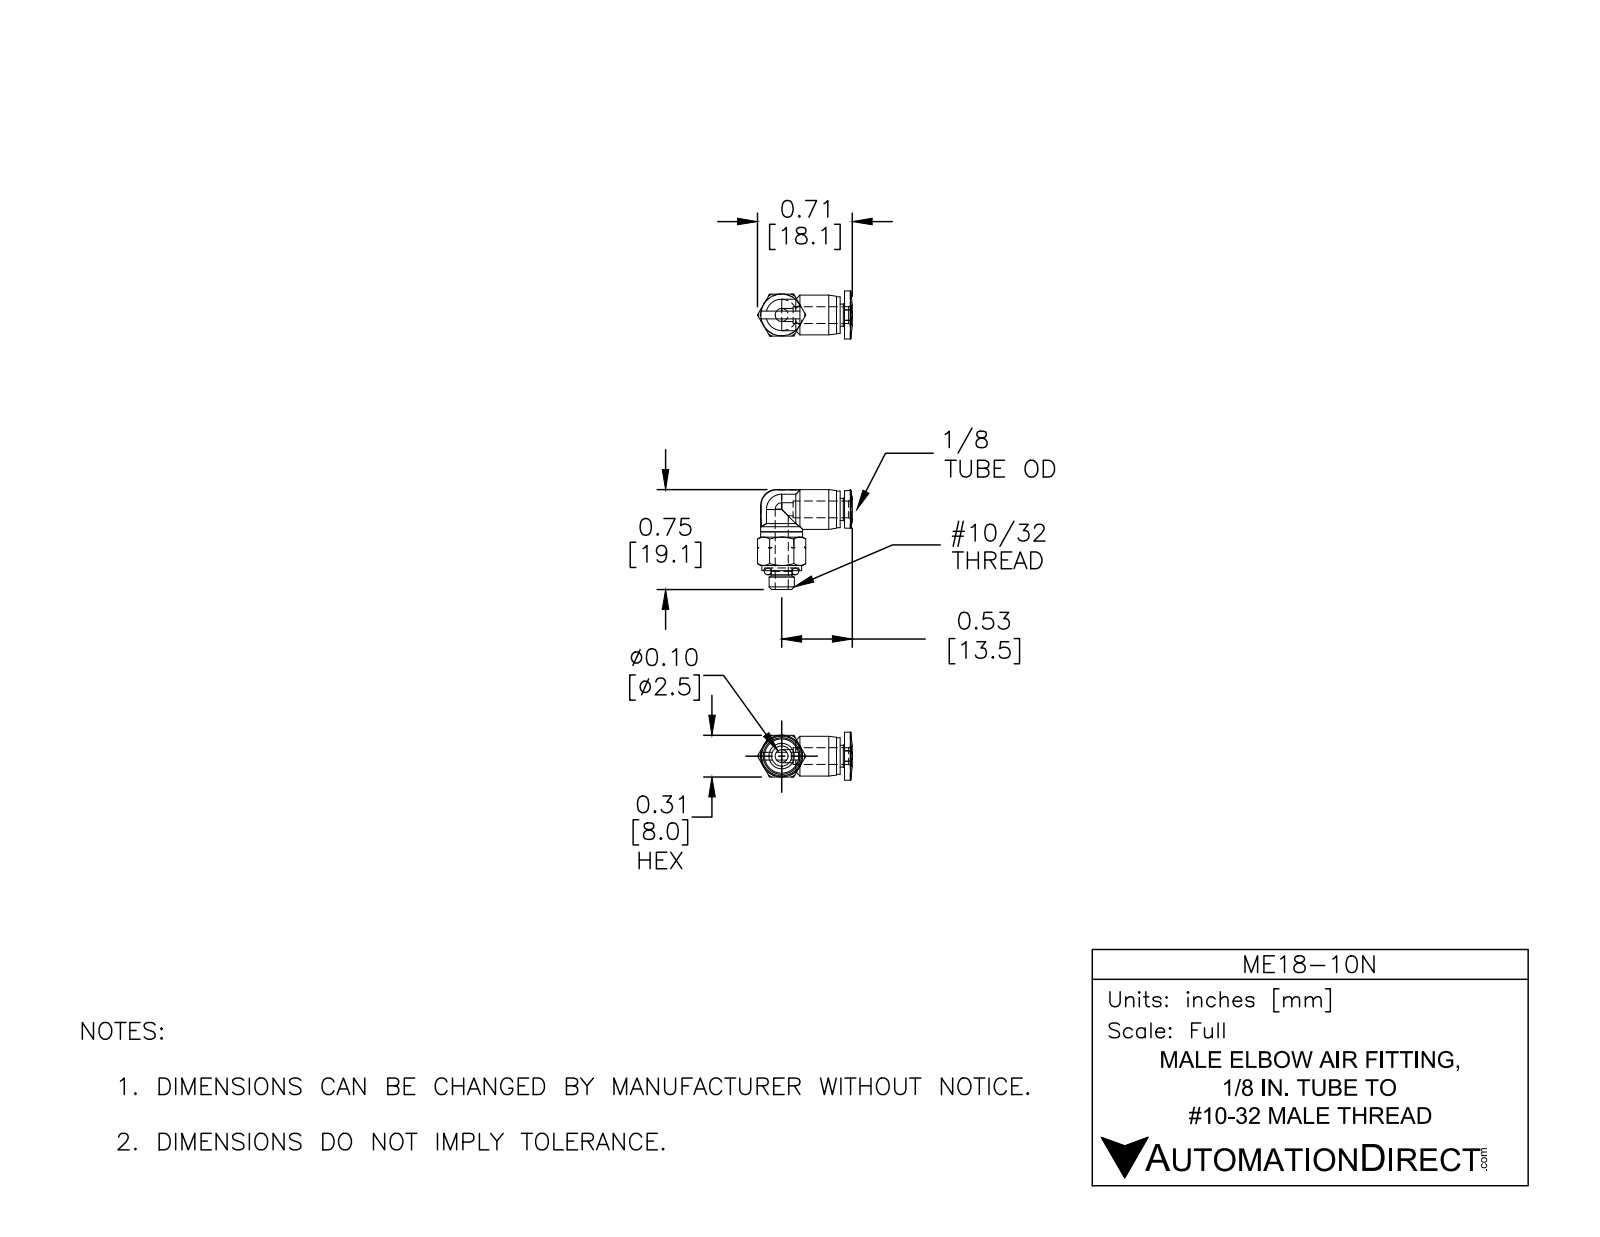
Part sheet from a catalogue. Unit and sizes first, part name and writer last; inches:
Units: inches
Overall size (bounding box): 0.752 × 0.713 × 0.362
Round holes (diameter × count): ⌀0.098 ×2, ⌀0.126 ×1
Round bosses / shafts (diameter × count): ⌀0.299 ×2, ⌀0.315 ×1, ⌀0.315 ×1, ⌀0.276 ×1, ⌀0.19 ×1, ⌀0.165 ×1, ⌀0.156 ×1
Partial cylindrical surfaces — rounded edges, fillets, slot ends (radius × count): R0.118 ×2, R0.142 ×2
Main face-to-face distances: 0.315, 0.031, 0.128, 0.187, 0.059, 0.02, 0.142, 0.161, 0.181, 0.039
Volume: 0.06 in³ · Surface area: 1.797 in²
Bodies: 2 solids, 116 faces (21 planar, 32 cylindrical, 63 other)
Part name (STEP PRODUCT): ME18-10N
STEP written by: SolidWorks 2015 (CONFIG_CONTROL_DESIGN)
